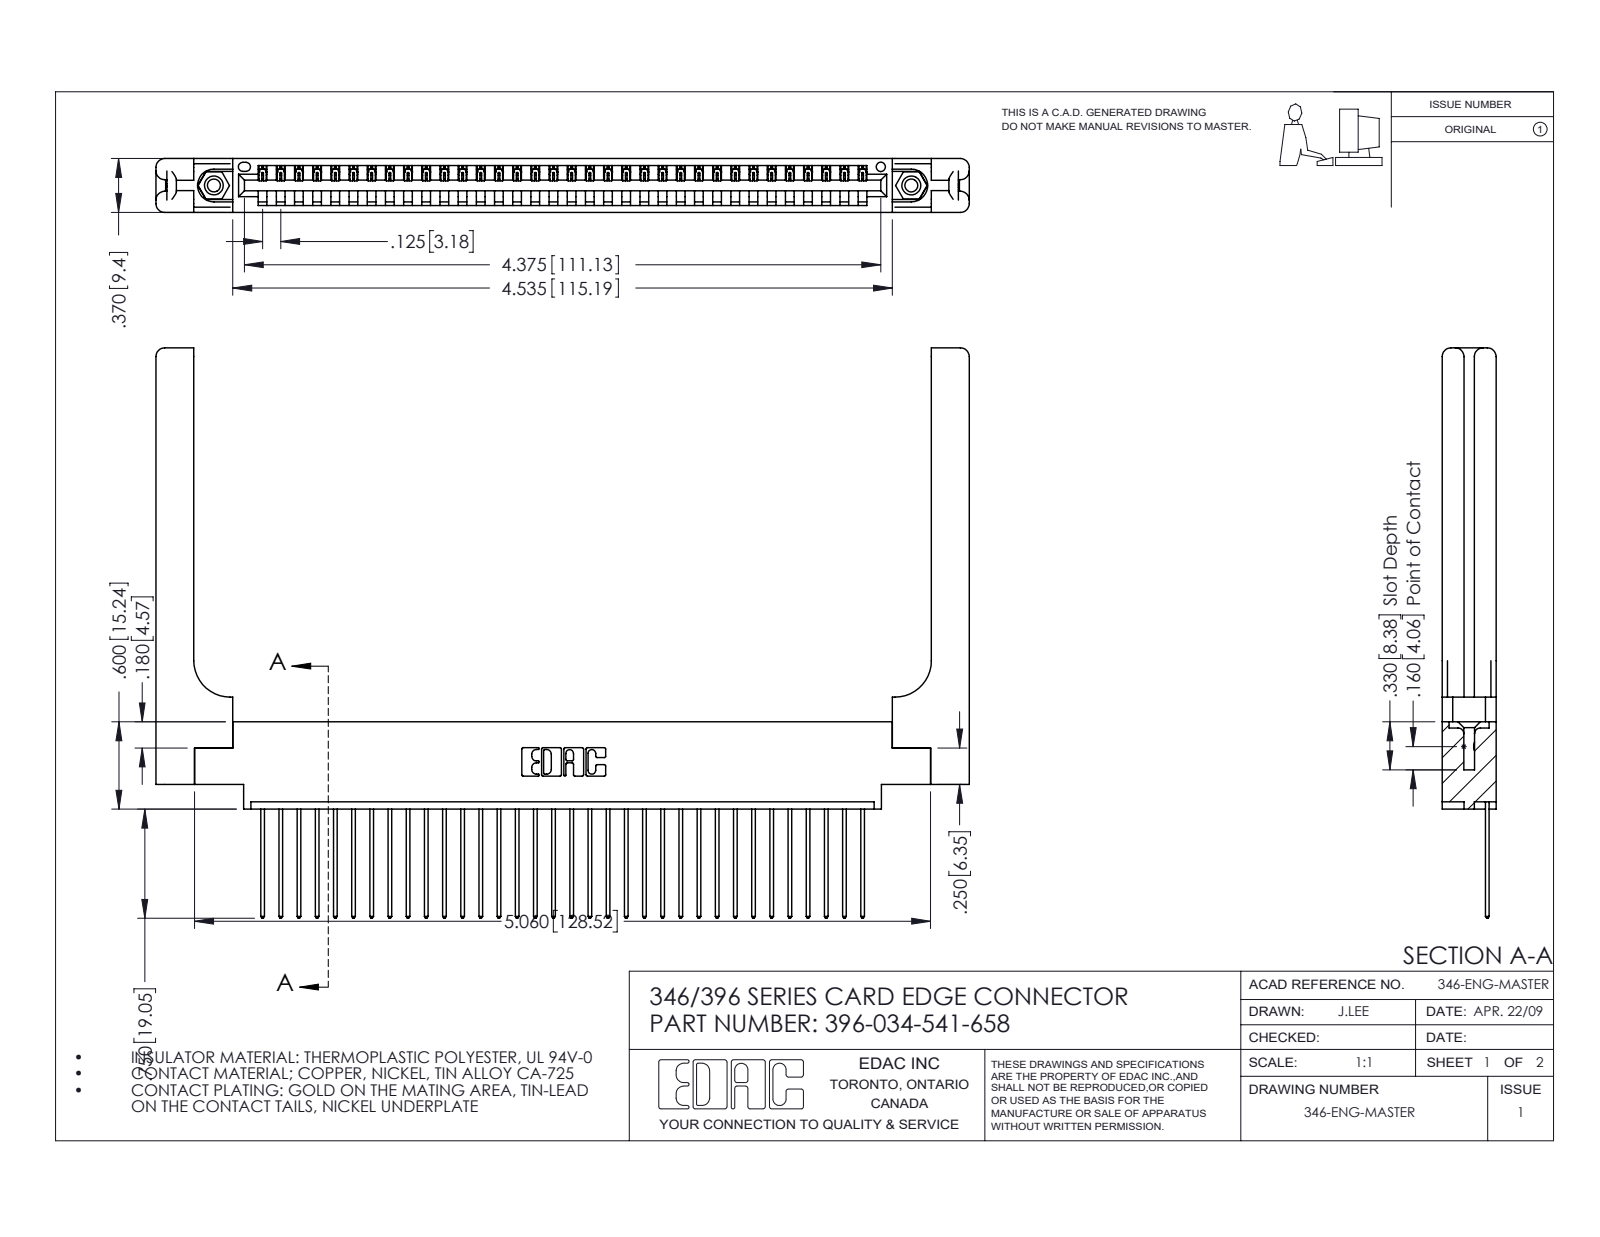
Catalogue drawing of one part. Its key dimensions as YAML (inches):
part_name: "346 Part_0.170 Offset - 0.156 Dia-TH; 346-220-058_345-220-058; 345-292-001_345-293-141; 345-250-001_345-250-001-102 (+1 more)"
step_written_by: "SolidWorks 2016 (CONFIG_CONTROL_DESIGN)"
units: inches
bodies: {solids: 39, faces: 2354, planar: 1588, cylindrical: 706, other: 60}
overall_size: [5.591, 3.92, 0.37]
volume: 1.282
surface_area: 35.31
round_holes:
  - {diameter: 0.089, count: 2}
  - {diameter: 0.125, count: 2}
  - {diameter: 0.156, count: 2}
  - {diameter: 0.064, count: 1}
round_bosses_or_shafts:
  - {diameter: 0.155, count: 2}
partial_cylinders:
  - {radius: 0.006, count: 68}
  - {radius: 0.01, count: 68}
  - {radius: 0.01, count: 22}
  - {radius: 0.06, count: 16}
  - {radius: 0.007, count: 6}
  - {radius: 0.031, count: 6}
  - {radius: 0.026, count: 3}
  - {radius: 0.03, count: 2}
face_to_face_distances: [0.37, 0.048, 0.322, 0.072, 0.148, 0.15, 0.298, 0.025, 0.25, 0.222]
hole_center_spacings: [0.246, 4.587, 4.795]
